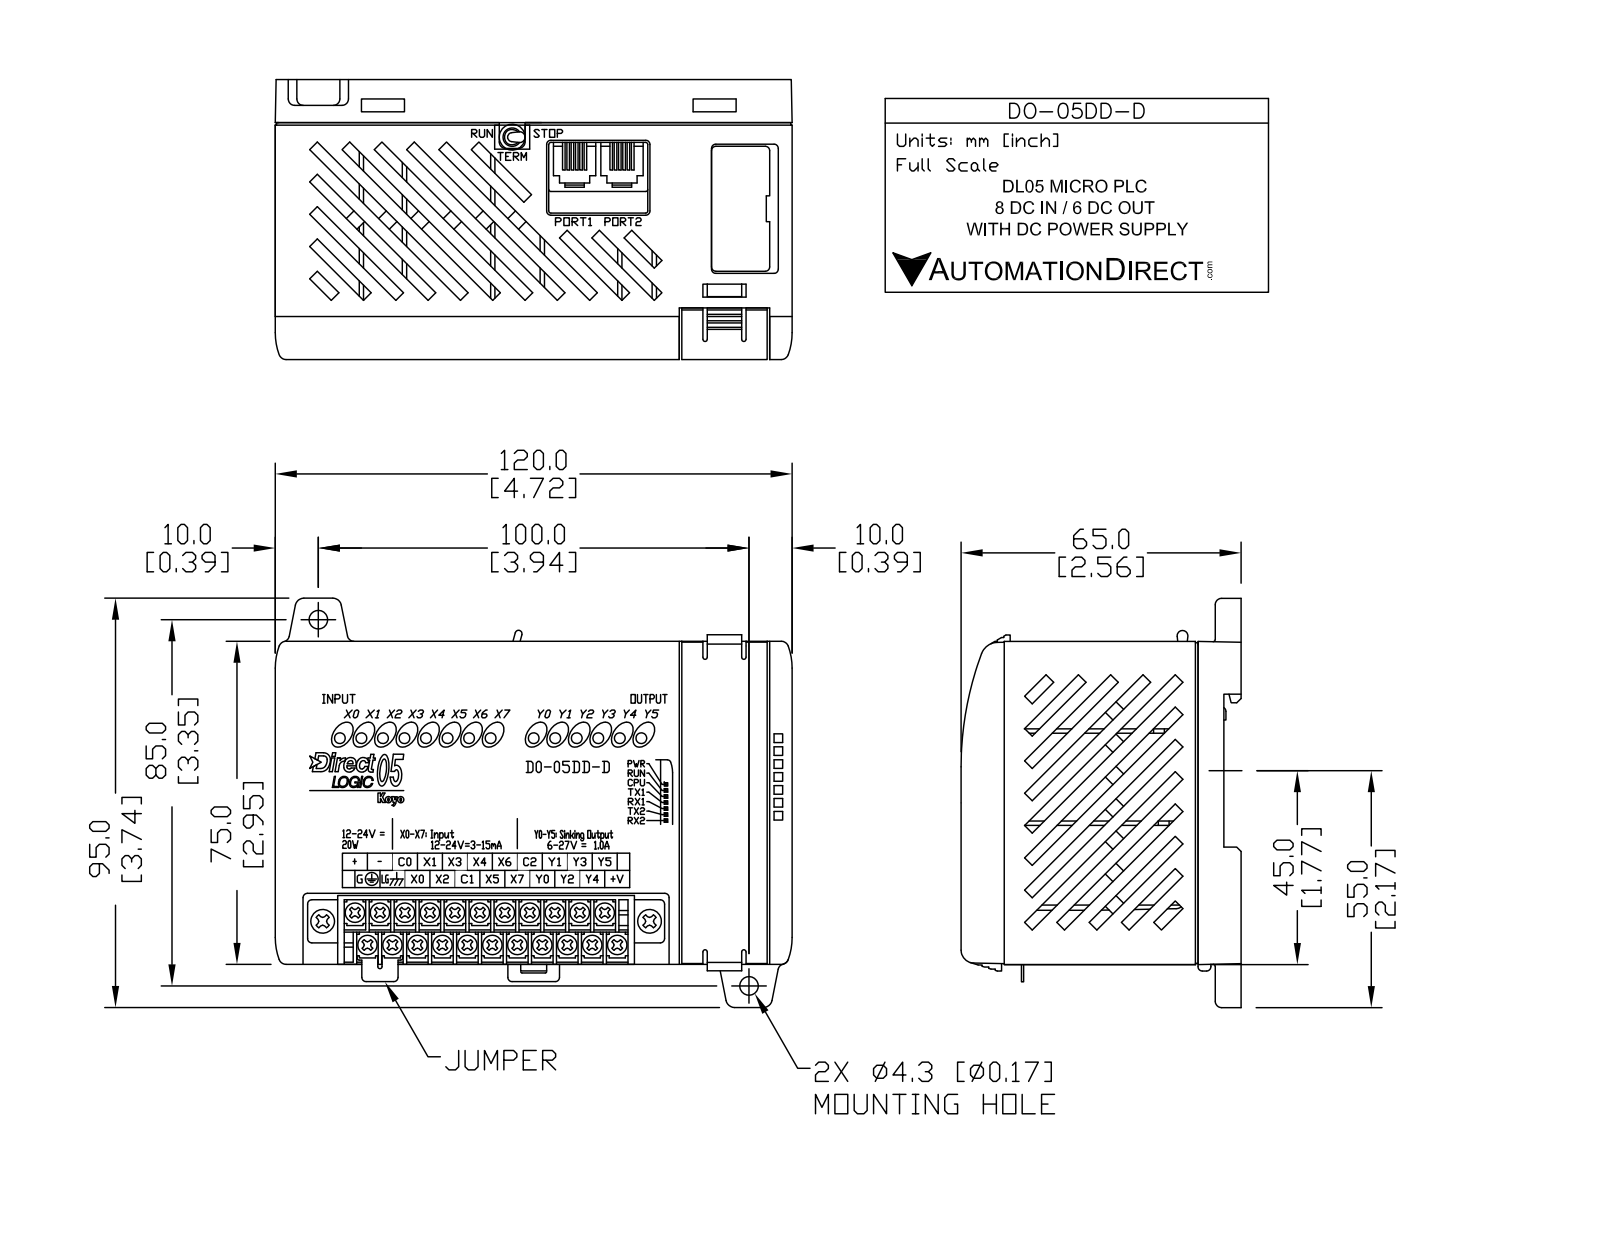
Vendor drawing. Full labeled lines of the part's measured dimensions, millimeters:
Part name (STEP PRODUCT): D0-05DD-D
STEP written by: SolidWorks 2009 (AUTOMOTIVE_DESIGN)
Units: millimetres
Bodies: 3 solids, 1010 faces (684 planar, 95 cylindrical, 231 other)
Overall size (bounding box): 120 × 95 × 65.06
Volume: 65 415 mm³ · Surface area: 91 010 mm²
Round holes (diameter × count): ⌀4.3 ×2
Round bosses / shafts (diameter × count): ⌀4.42 ×22, ⌀4.5 ×2
Partial cylindrical surfaces — rounded edges, fillets, slot ends (radius × count): R1 ×4, R2 ×4, R1.5 ×2, R63.5 ×1, R65 ×1
Main face-to-face distances: 1.5, 73.5, 59.5, 4, 63.5, 118.5, 75, 72, 5.5, 65
Hole centre spacings: 131.24
